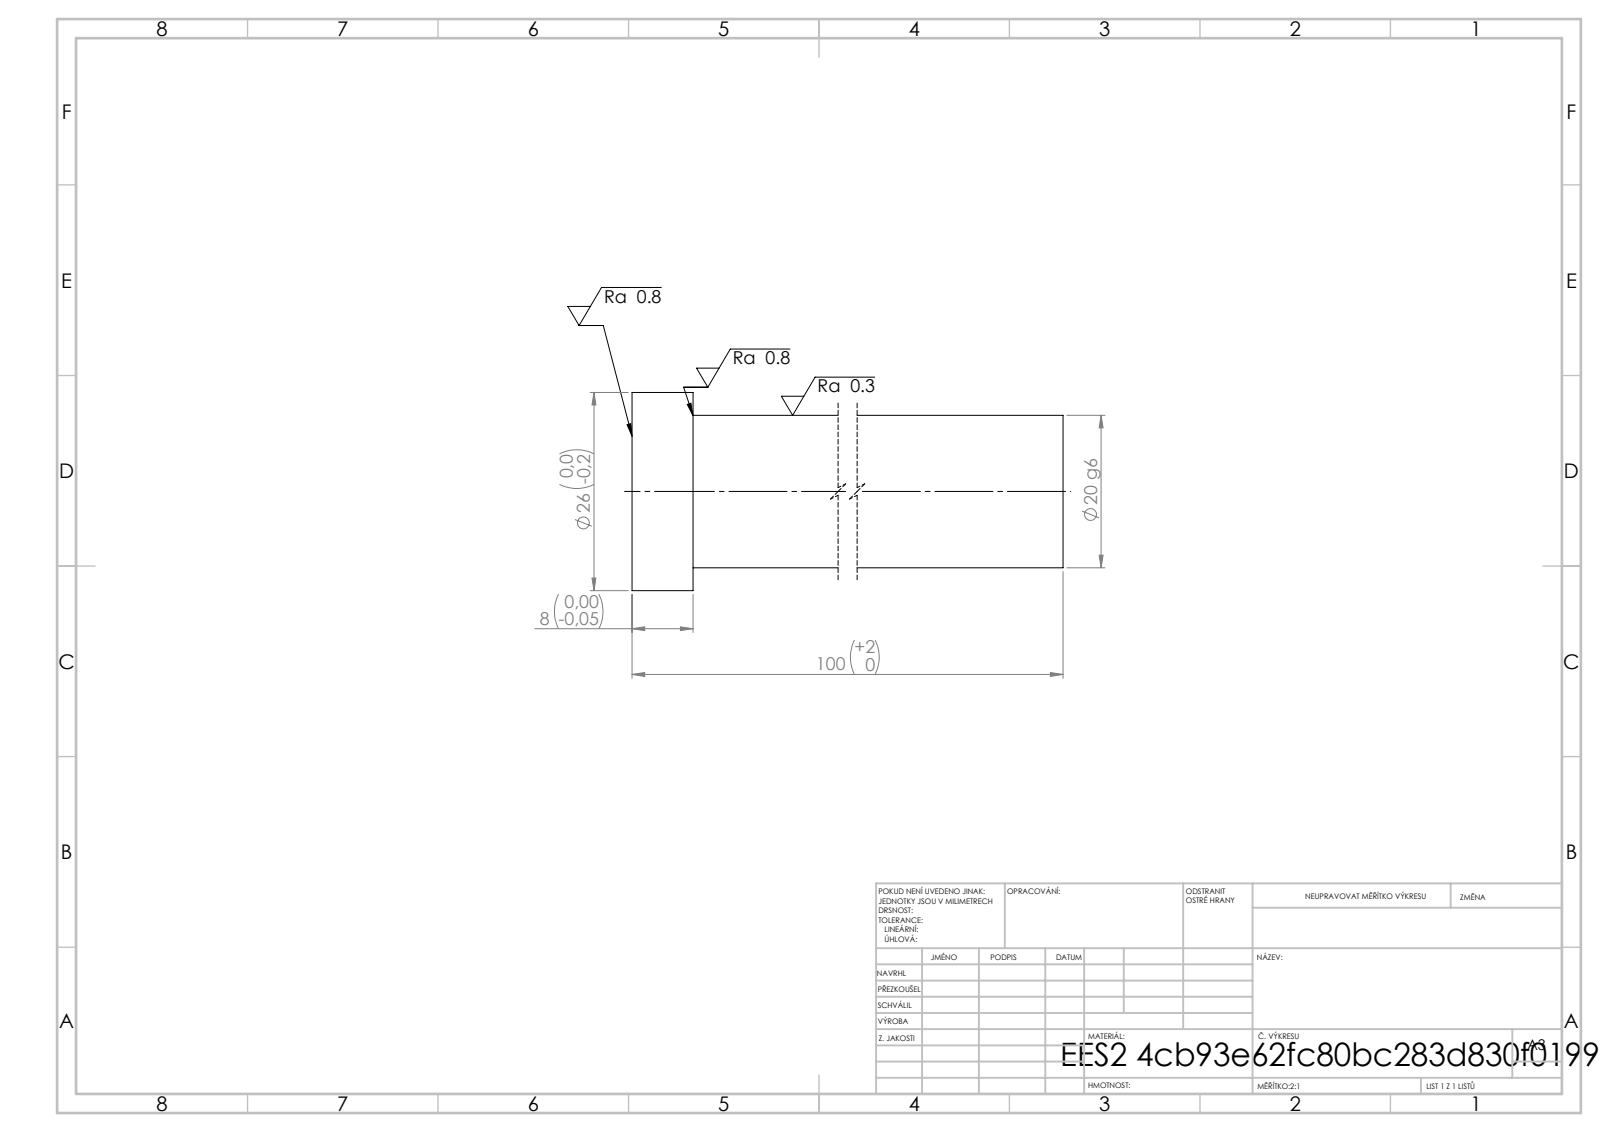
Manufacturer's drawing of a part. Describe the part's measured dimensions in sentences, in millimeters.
Its 3-D file was written by "SolidWorks 2019 (CONFIG_CONTROL_DESIGN)". It is 1 solid with 7 faces: 3 planar, 4 cylindrical and 0 other. Overall it measures 100 by 26 by 26 millimeters. Its volume is 33 150 cubic millimeters and its surface area 7 496 square millimeters. Round bosses or shafts: 1 of diameter 26, 1 of diameter 20. The main face-to-face distances are 100, 8, 92.
